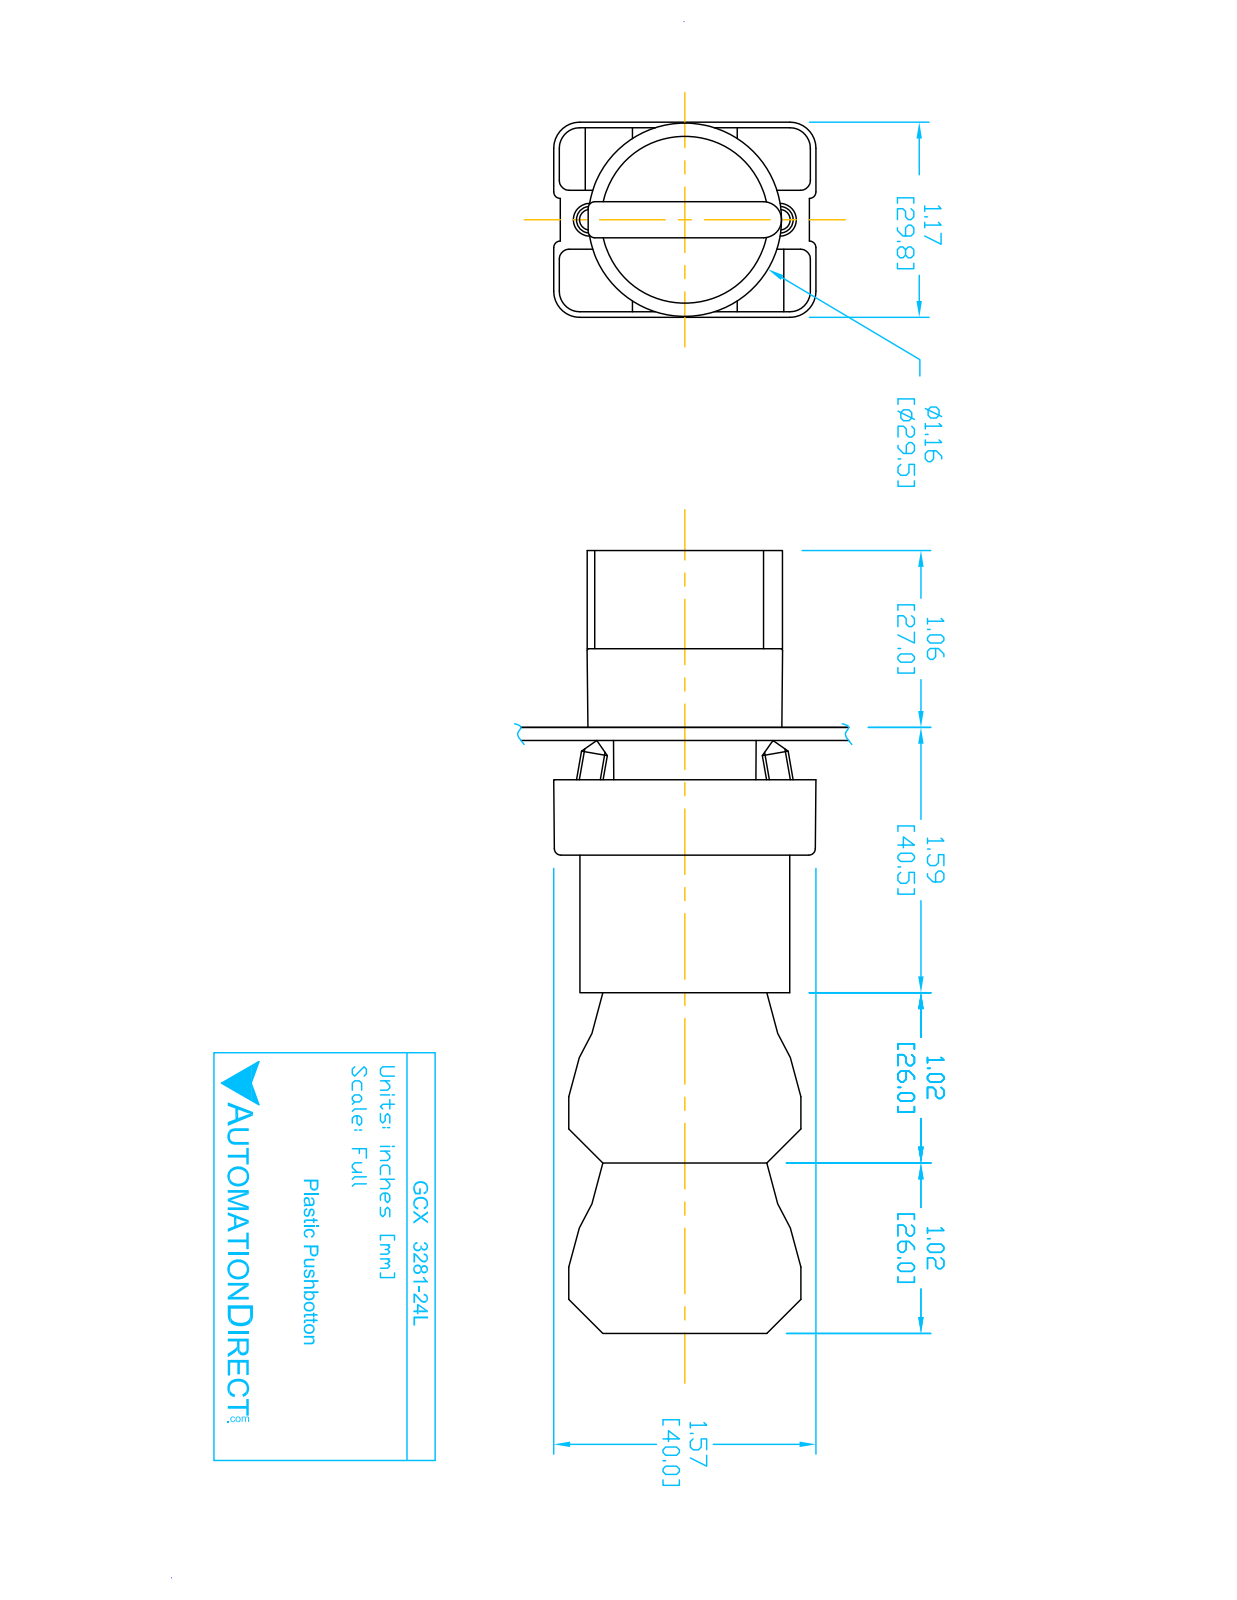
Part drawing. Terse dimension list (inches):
name: ECX1050; ecx1040; ecx1030; ECX3029-2 (+2 more)
written by: SolidWorks 2016 (AUTOMOTIVE_DESIGN)
unit: in
bodies: 11 solids, 724 faces (488 planar, 193 cylindrical, 43 other)
size: 4.677 × 1.581 × 1.177
volume: 4.751 in³; area: 59.22 in²
holes: 4× ⌀0.079, 2× ⌀0.087, 2× ⌀0.124, 2× ⌀0.13, 1× ⌀0.197, 1× ⌀0.469, 1× ⌀0.878, 1× ⌀0.888, 1× ⌀1.024
bosses: 4× ⌀0.157, 1× ⌀1.175, 1× ⌀1.004, 1× ⌀0.945, 1× ⌀0.856, 1× ⌀0.78, 1× ⌀0.504
rounds: 24× R0.059, 12× R0.041, 12× R0.124, 12× R0.157, 9× R0.039, 2× R0.02, 2× R0.063, 2× R0.079
face distances: 0.579, 0.593, 1.024, 1.171, 0.014, 0.827, 1.85, 3.043, 2.02, 1.193
hole spacings: 0.236, 1.003, 0.974, 0.472, 0.539, 0.544, 1.083, 0.484
